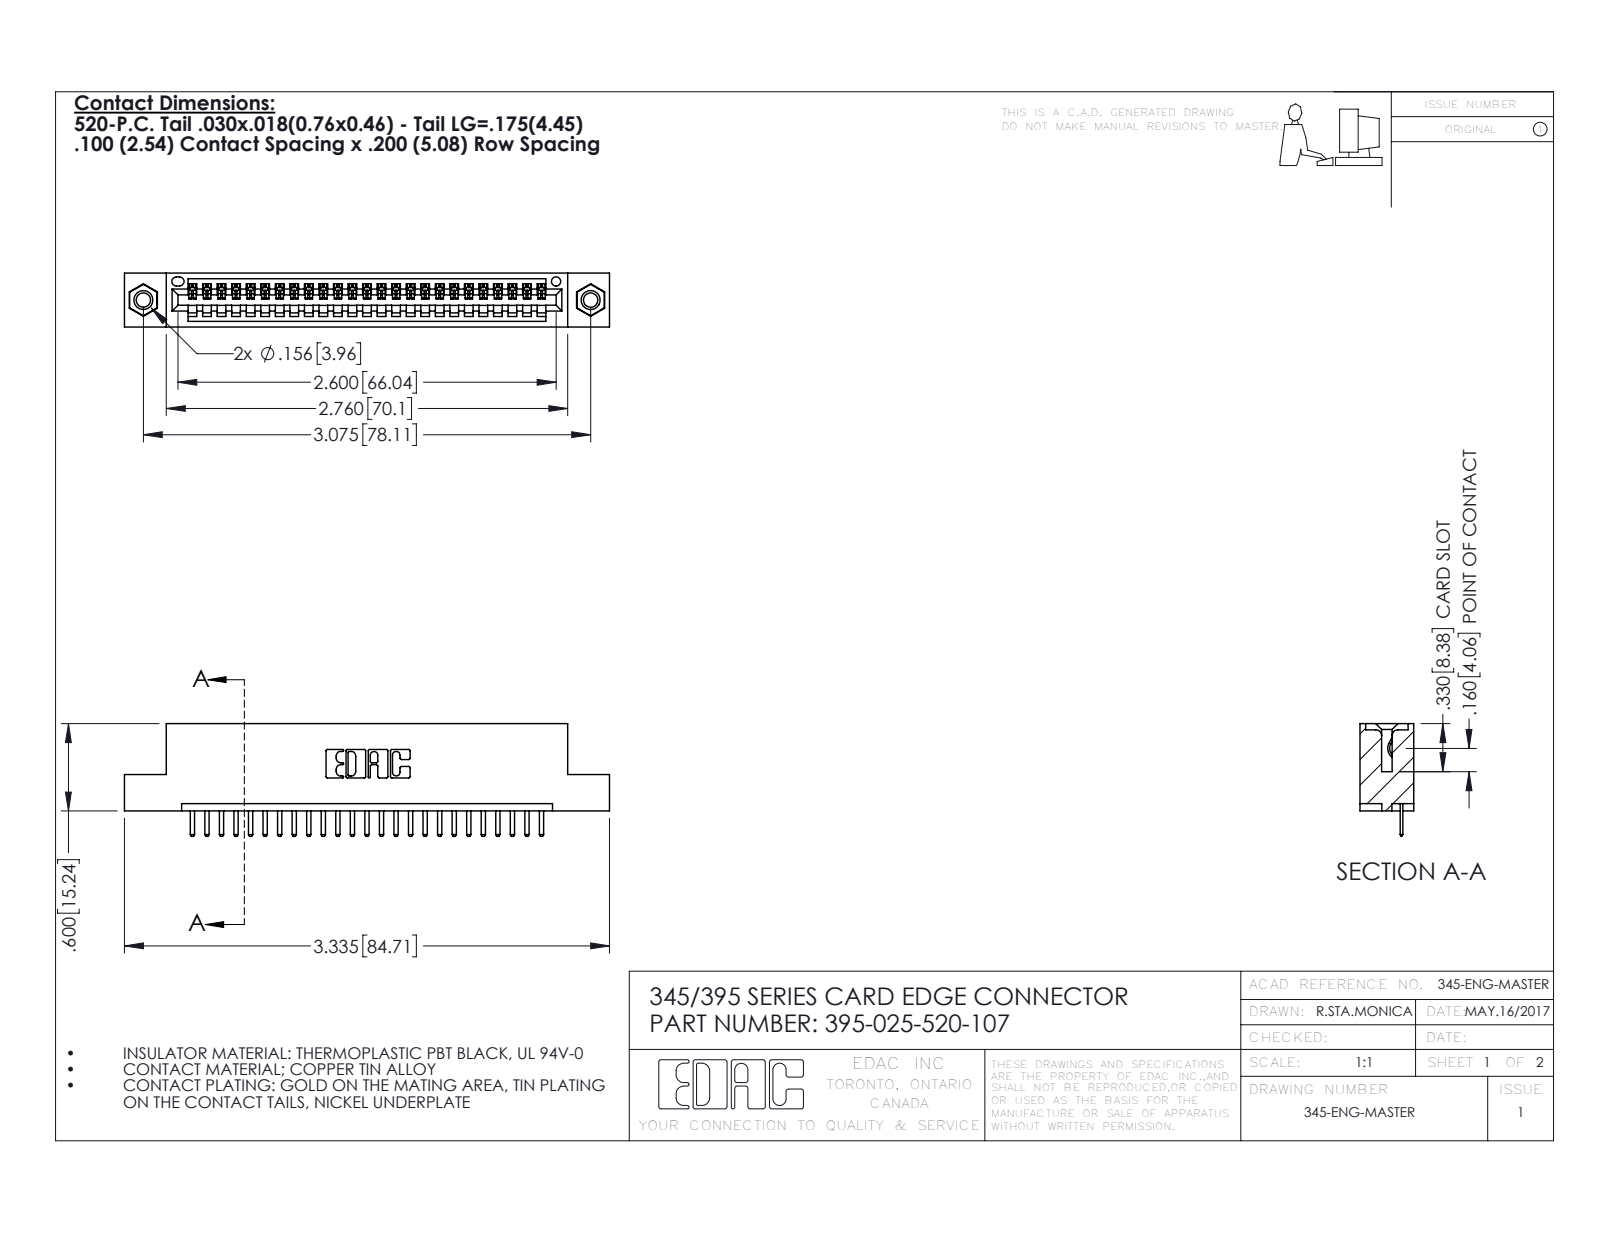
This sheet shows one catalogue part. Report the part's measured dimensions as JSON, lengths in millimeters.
{"part_name": "395-025-520-107; 345-292-001_345-293-120; 345-250-001_345-250-005-103; 345 Part_Flush Mounting Lugs - 0.156 Dia-TI", "step_written_by": "SolidWorks 2016 (CONFIG_CONTROL_DESIGN)", "units": "millimeters", "bodies": {"solids": 28, "faces": 1736, "planar": 1162, "cylindrical": 558, "other": 16}, "overall_size": [84.7, 19.7, 9.4], "volume_mm3": 7820, "surface_area_mm2": 9961, "round_holes": [[2.5, 2], [3.2, 2], [4, 2], [1.6, 1]], "round_bosses_or_shafts": [[3.9, 2]], "partial_cylinders_radius": [[0.3, 52], [0.2, 50], [0.3, 22], [0.2, 6], [0.8, 6], [0.7, 3], [0.8, 2], [1, 2]], "face_to_face_distances": [1.8, 7.6, 9.4, 5.1, 2.5, 6.9, 0.6, 5.7, 1.8, 3.8], "hole_center_spacings": [6.9, 72.1, 78.1]}
